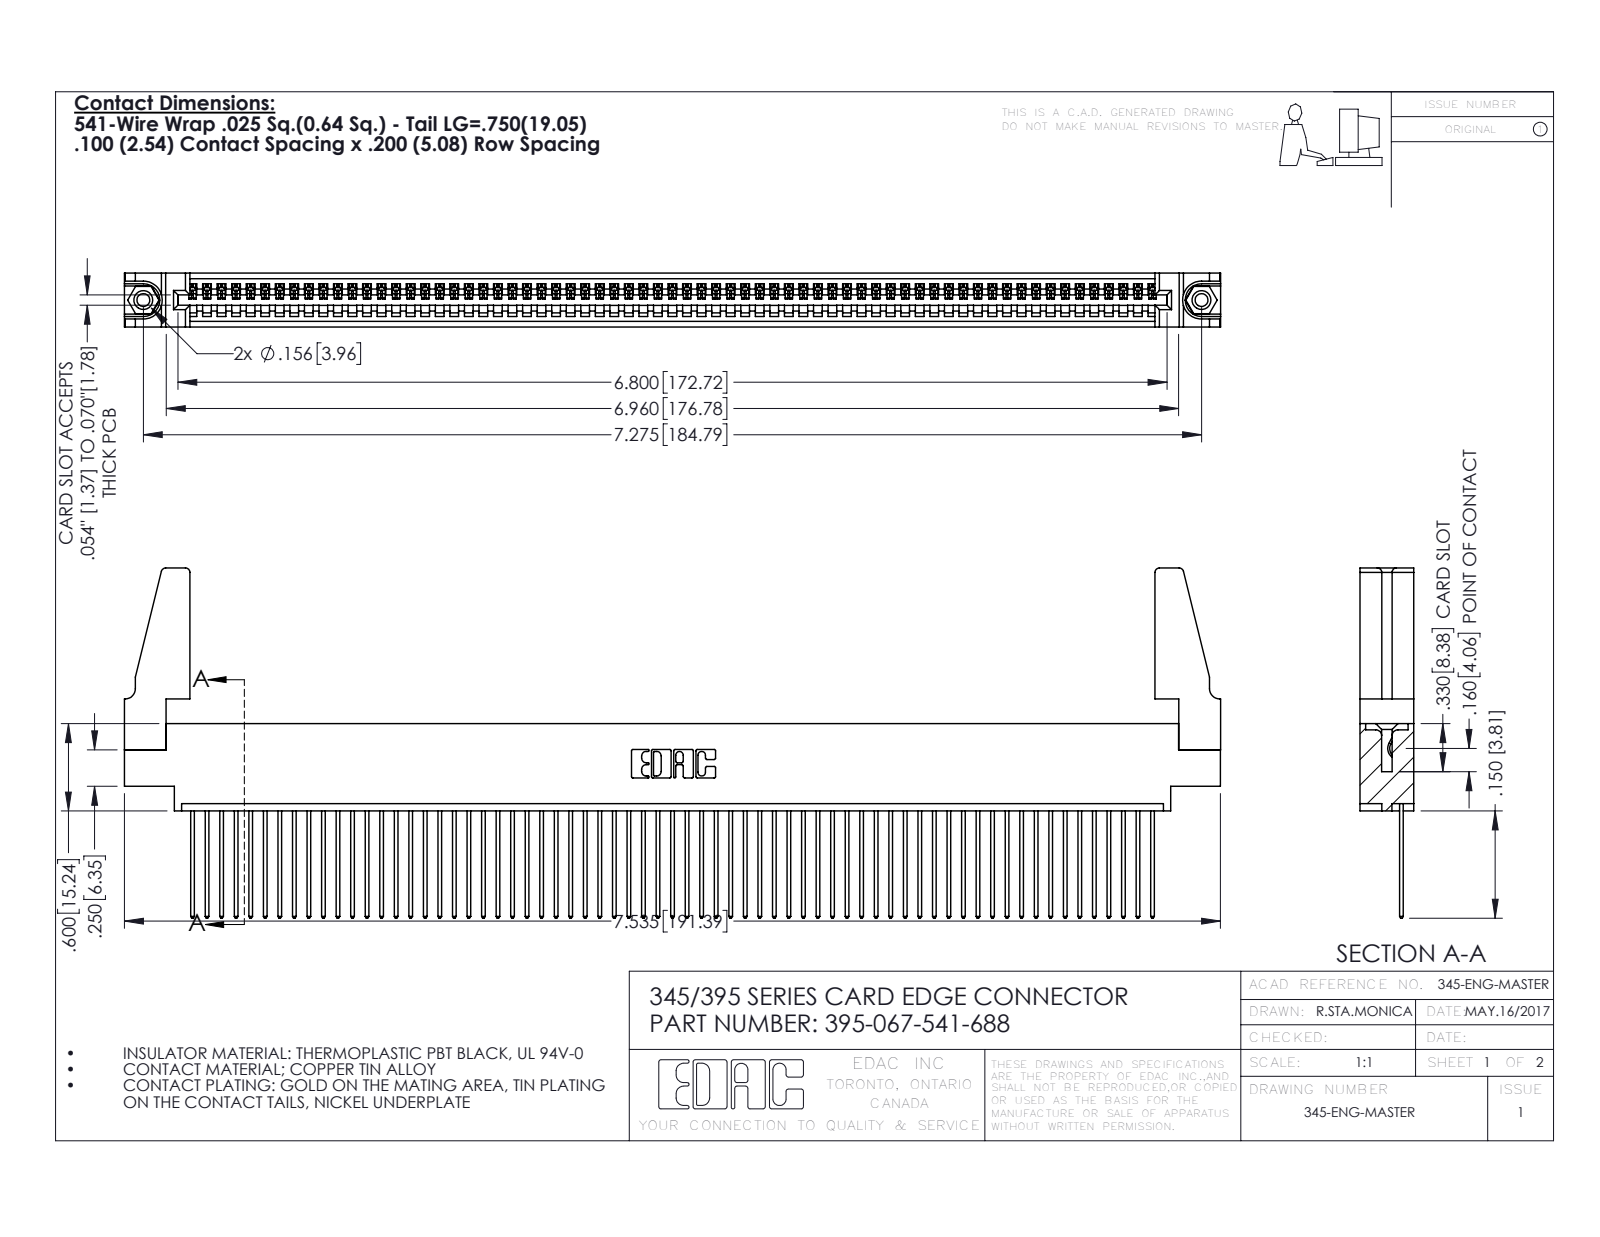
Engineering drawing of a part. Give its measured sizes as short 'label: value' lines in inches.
name: 395-067-541-688; 345-250-001_345-250-001-102; 345-220-078_345-220-088; 345-292-001_345-293-141 (+1 more)
written by: SolidWorks 2016 (CONFIG_CONTROL_DESIGN)
unit: in
bodies: 72 solids, 4140 faces (2836 planar, 1288 cylindrical, 16 other)
size: 7.536 × 2.407 × 0.37
volume: 1.327 in³; area: 45.68 in²
holes: 2× ⌀0.089, 2× ⌀0.125, 2× ⌀0.156, 1× ⌀0.064
bosses: 2× ⌀0.155
rounds: 134× R0.006, 134× R0.01, 22× R0.01, 8× R0.03, 6× R0.007, 6× R0.031, 3× R0.026, 2× R0.031
face distances: 0.072, 0.298, 0.37, 0.098, 0.272, 0.025, 0.2, 0.225, 0.175, 0.149
hole spacings: 0.27, 7.039, 7.275
